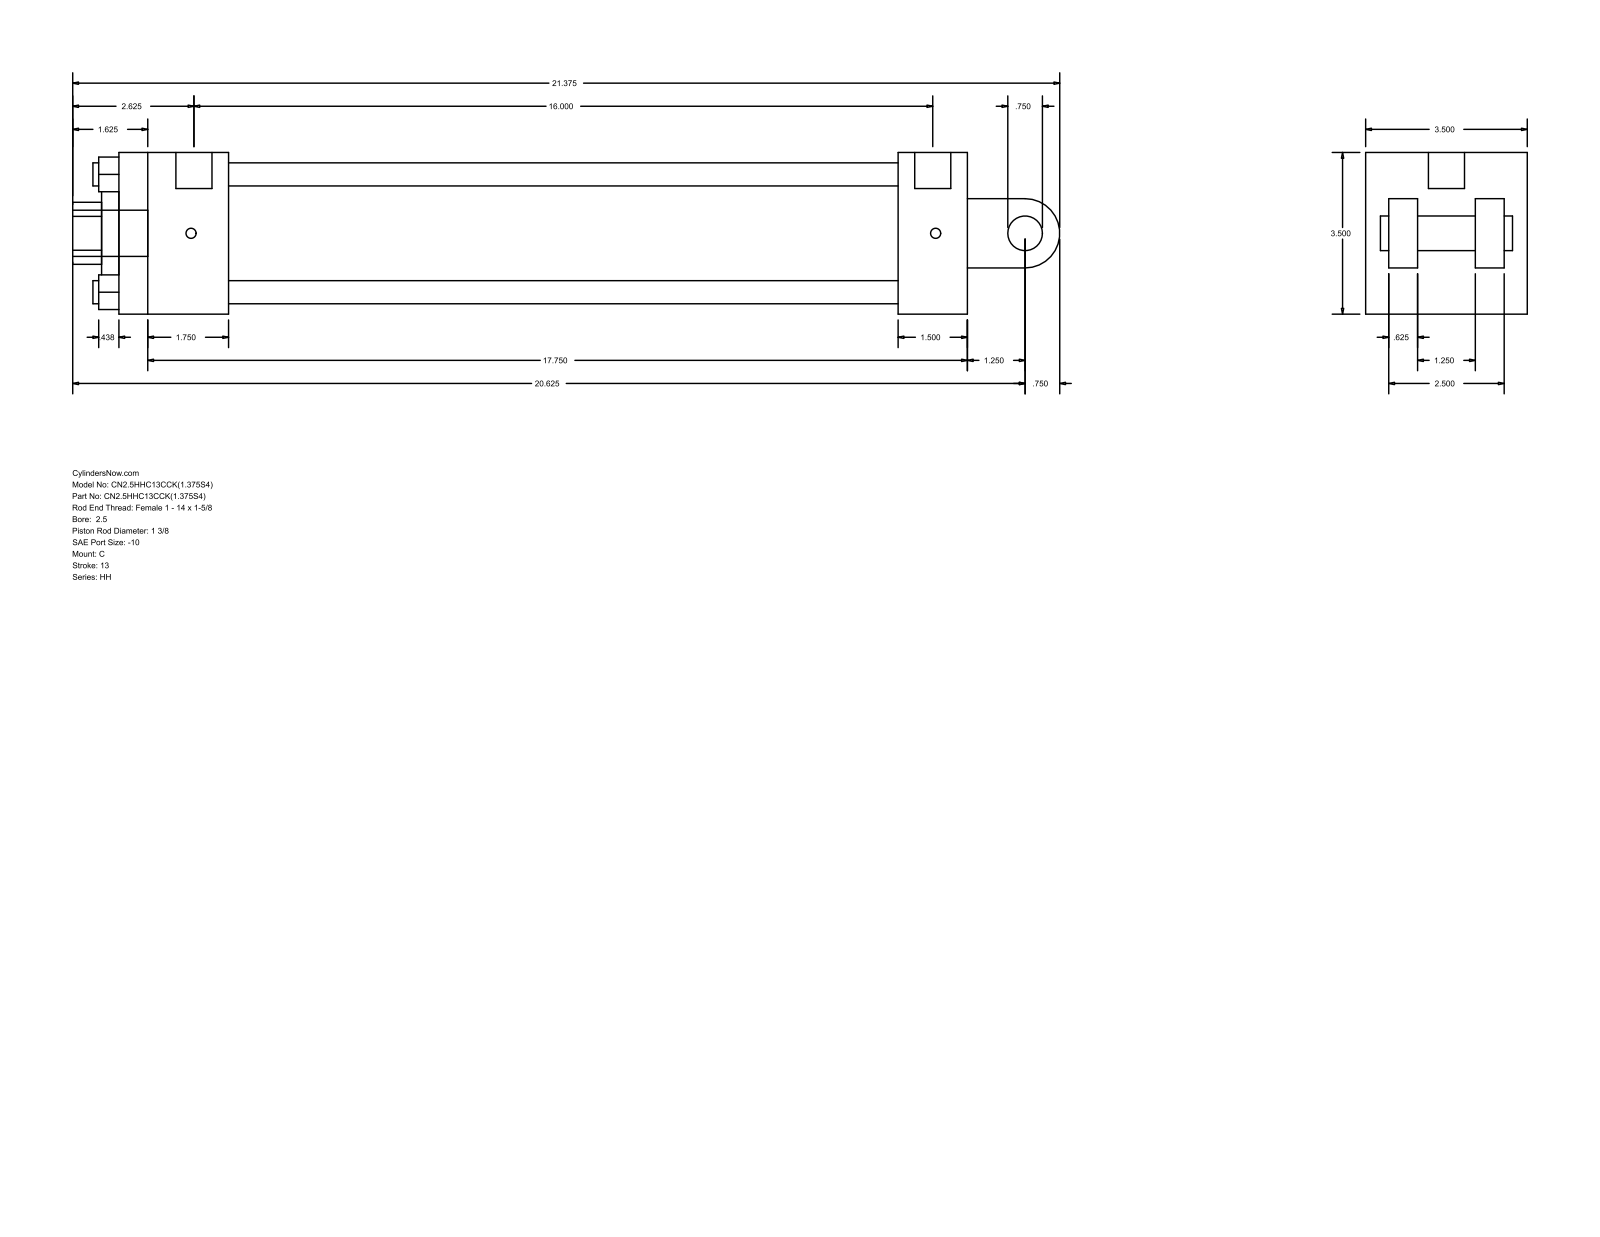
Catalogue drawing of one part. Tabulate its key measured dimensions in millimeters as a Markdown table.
| quantity | value |
| --- | --- |
| part name | HH_C__0250_1.375 |
| STEP written by | GSSL Pune (CONFIG_CONTROL_DESIGN) |
| units | millimeters |
| bodies | 0 solids, 99 faces (70 planar, 29 cylindrical, 0 other) |
| overall size | 542.92 × 88.9 × 88.9 |
| round holes (diameter × count) | 12.7 × 4, 5.56 × 2, 19.84 × 1, 34.92 × 1, 50.8 × 1, 73.03 × 1 |
| round bosses / shafts (diameter × count) | 5.56 × 2, 25.4 × 1, 19.84 × 1, 19.05 × 1 |
| partial cylindrical surfaces (radius × count) | 17.06 × 1, 19.05 × 1 |
| main face-to-face distances | 88.9, 466.72, 38.1, 63.5, 15.87, 12.7, 428.62, 60.32, 368.3, 406.4 |
| hole center spacings | 45.79, 64.76, 91.58, 1.59 |
